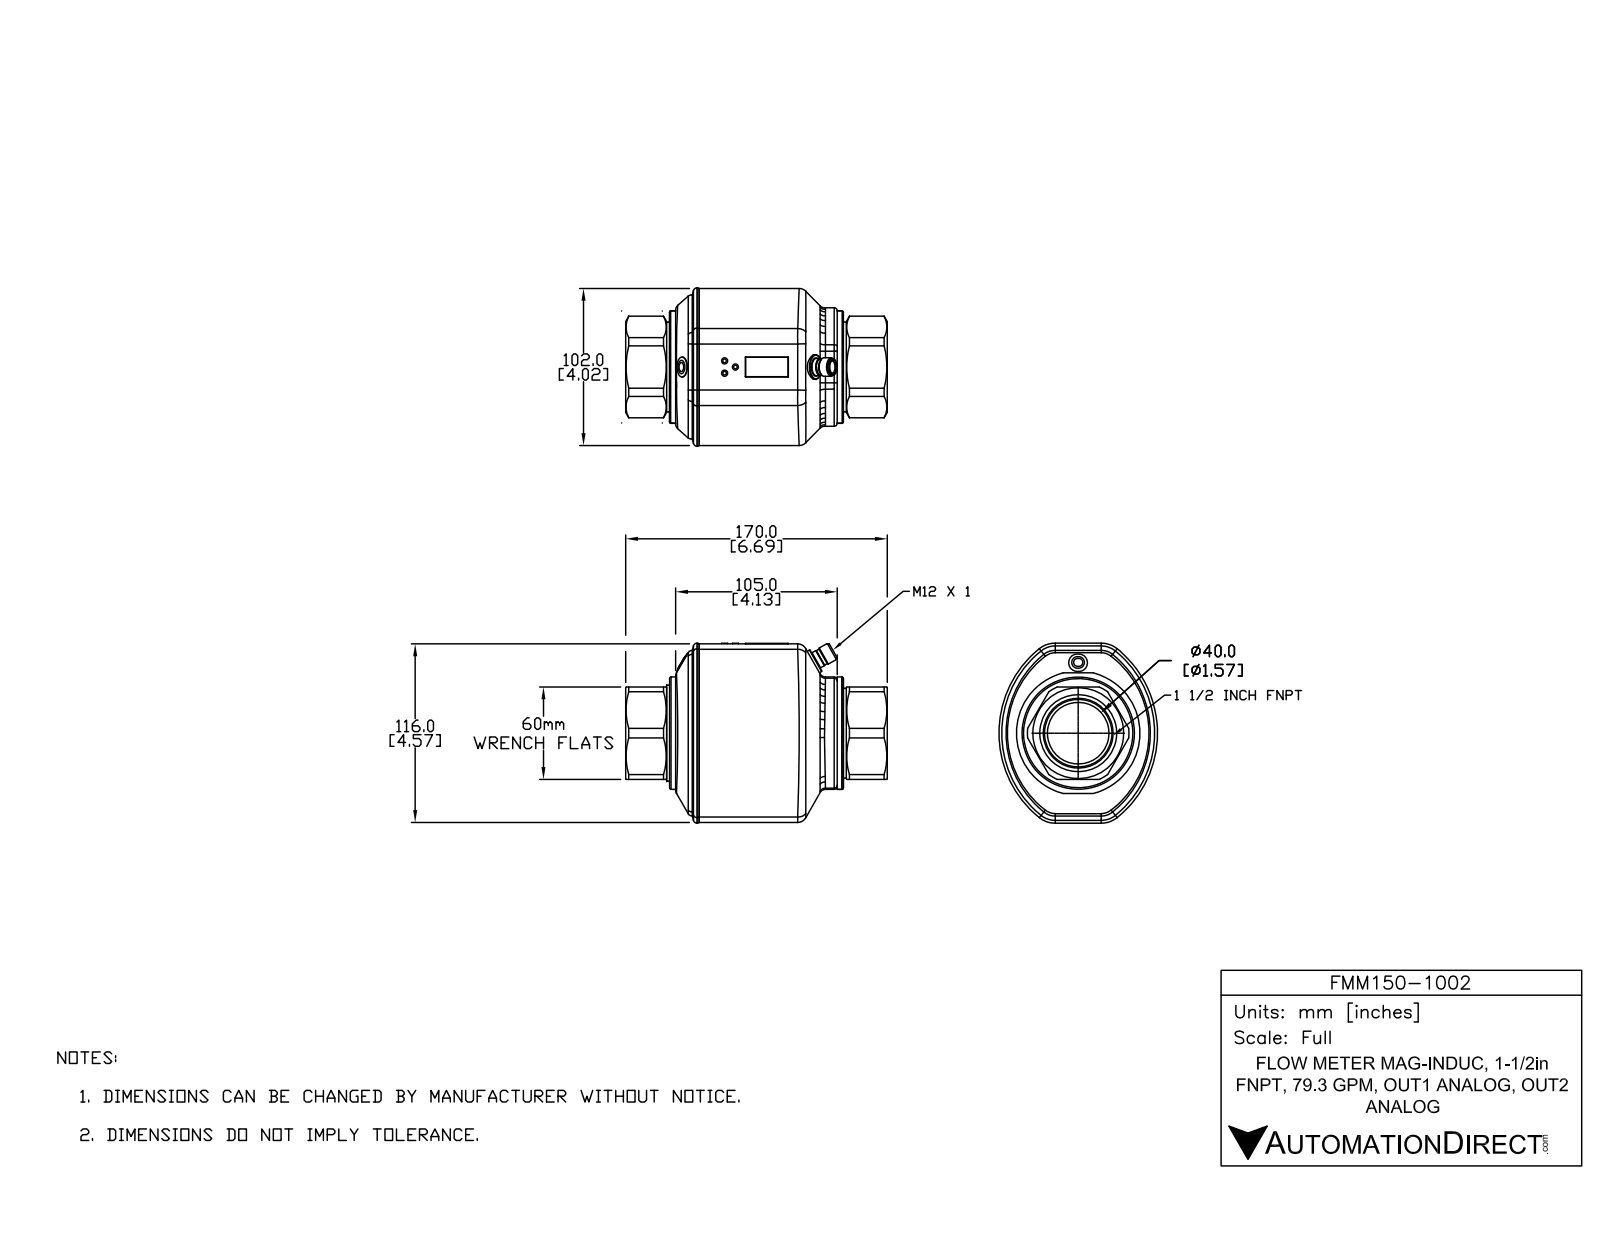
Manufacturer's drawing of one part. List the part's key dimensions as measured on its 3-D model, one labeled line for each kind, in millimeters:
Part name (STEP PRODUCT): FMM150-1002
STEP written by: SolidWorks 2015 (AUTOMOTIVE_DESIGN)
Units: millimetres
Bodies: 10 solids, 283 faces (69 planar, 84 cylindrical, 130 other)
Overall size (bounding box): 175.88 × 118.91 × 103
Volume: 1 081 000 mm³ · Surface area: 118 655 mm²
Round holes (diameter × count): ⌀8.4 ×1, ⌀40 ×1, ⌀44 ×1
Round bosses / shafts (diameter × count): ⌀4 ×3, ⌀12 ×2, ⌀3.9 ×2, ⌀73 ×1, ⌀60 ×1, ⌀14.9 ×1, ⌀11.3 ×1, ⌀10.6 ×1
Partial cylindrical surfaces — rounded edges, fillets, slot ends (radius × count): R0.9 ×4, R11 ×4, R16 ×4, R16.5 ×4, R1 ×2, R2 ×2, R70 ×2, R70.5 ×2
Main face-to-face distances: 23.91, 79.3, 103.21, 110.88, 31.58, 7.67, 60, 32.5, 143.38, 28
